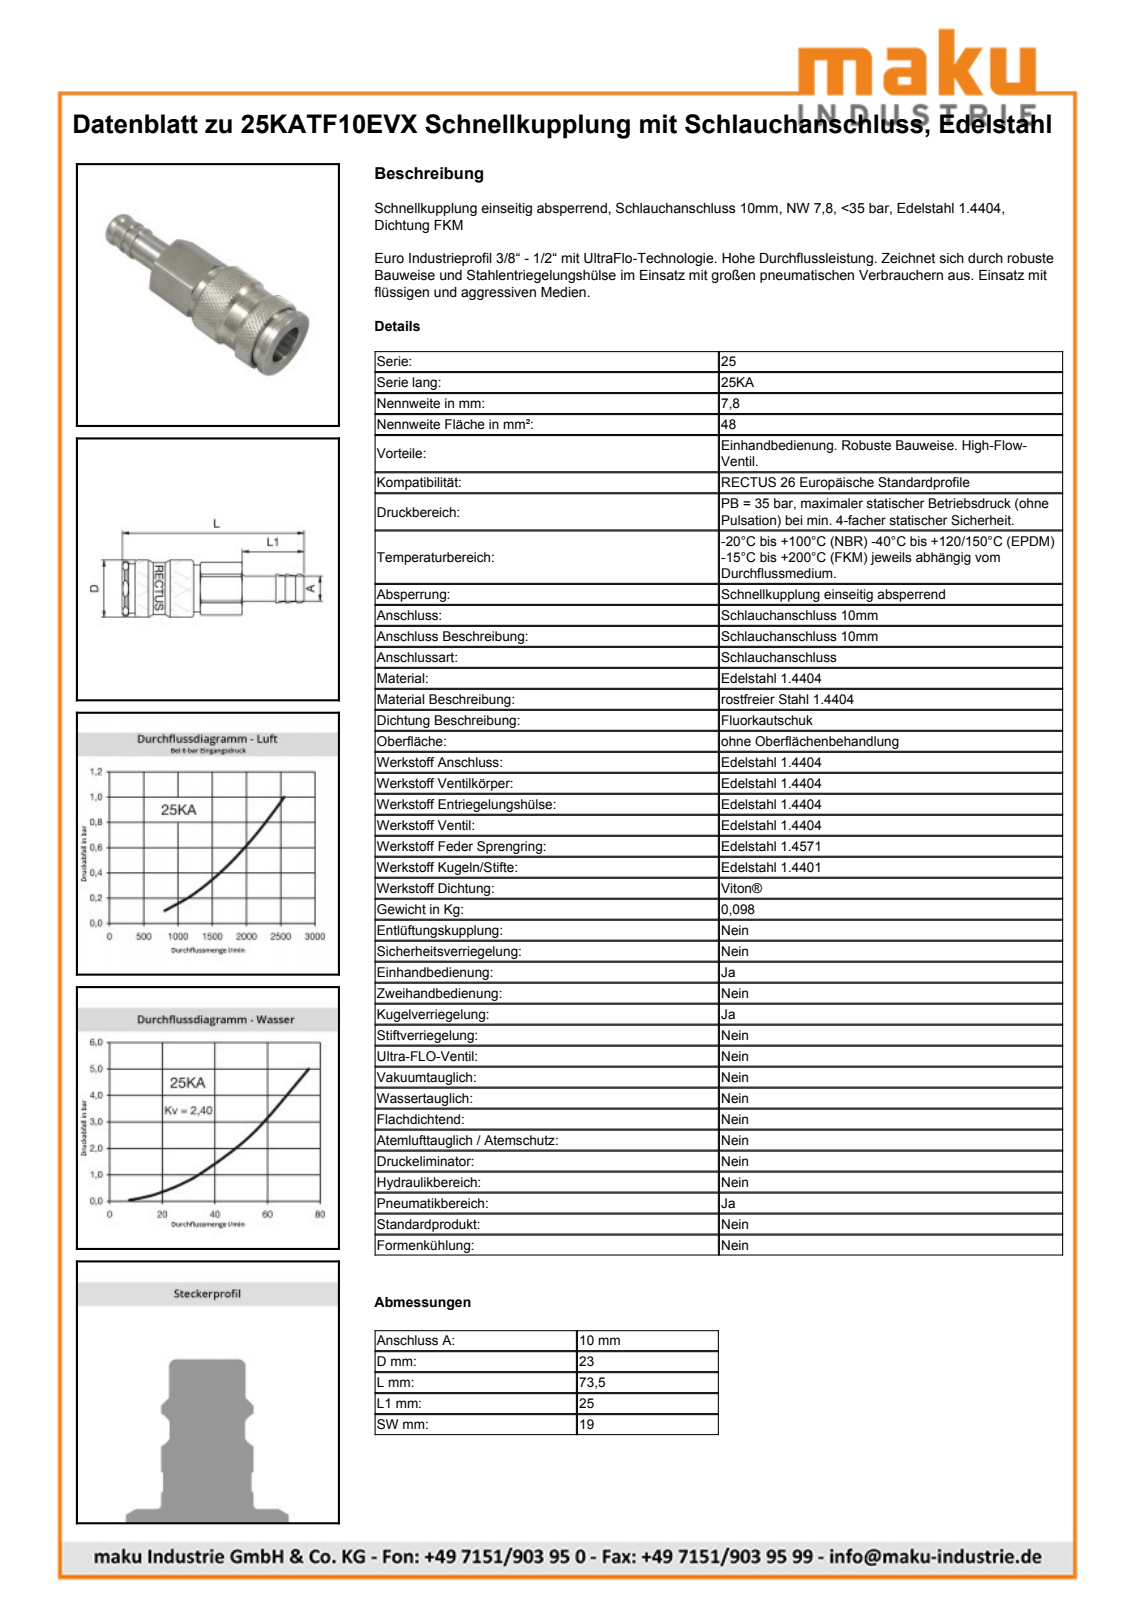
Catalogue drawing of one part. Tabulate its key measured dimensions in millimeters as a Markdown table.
| quantity | value |
| --- | --- |
| part name | D108220 |
| STEP written by | Autodesk Inventor 2013 (AUTOMOTIVE_DESIGN) |
| units | millimeters |
| bodies | 2 solids, 616 faces (213 planar, 84 cylindrical, 319 other) |
| overall size | 73.5 × 23.15 × 23.15 |
| volume | 17 981 mm³ |
| surface area | 8 467 mm² |
| round holes (diameter × count) | 15.1 × 1, 16 × 1, 17.25 × 1, 19.35 × 1, 20.05 × 1 |
| round bosses / shafts (diameter × count) | 23.15 × 1, 21 × 1, 20 × 1, 18.95 × 1, 15.3 × 1, 15 × 1, 14.5 × 1, 10.1 × 1 |
| partial cylindrical surfaces (radius × count) | 10.4 × 1, 10.7 × 1, 11 × 1 |
| main face-to-face distances | 19, 48.5, 24.5, 24, 73.5, 49, 25, 5.25, 19.25, 28.75 |
